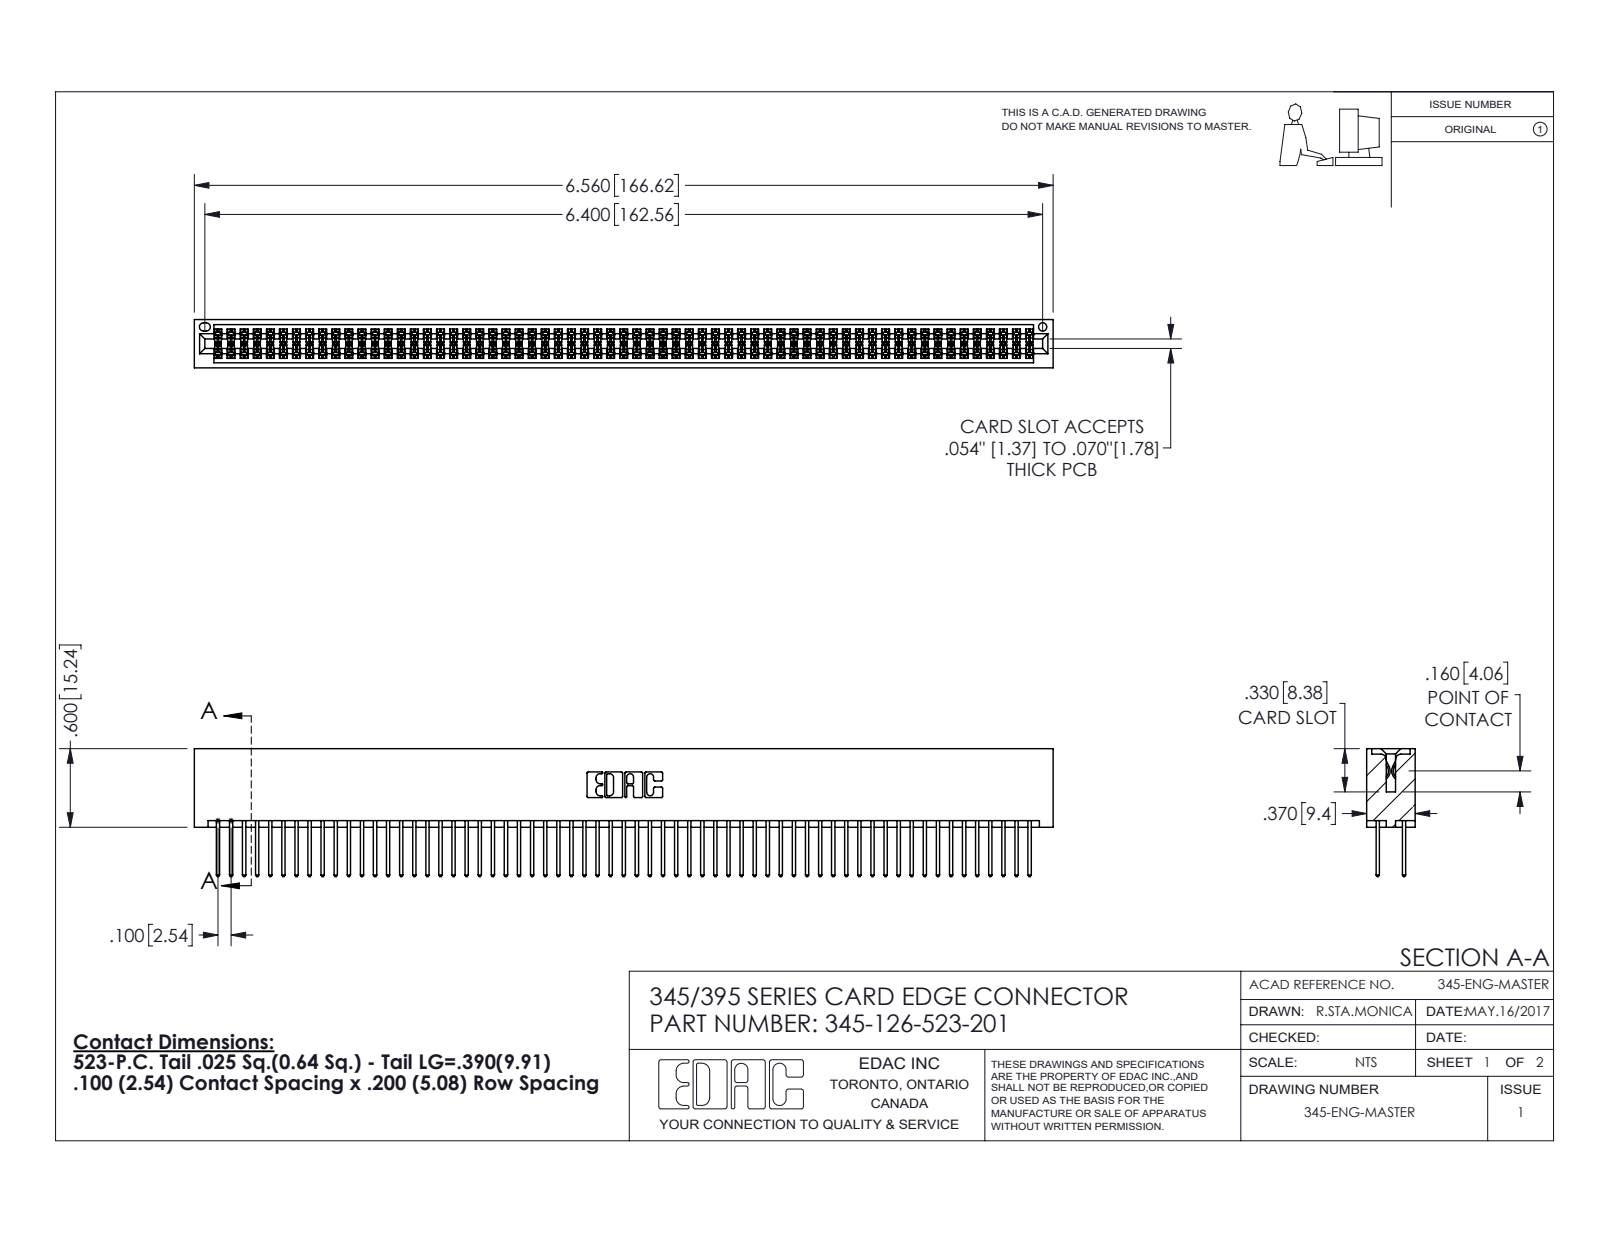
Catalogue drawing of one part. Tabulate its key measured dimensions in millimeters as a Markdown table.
| quantity | value |
| --- | --- |
| part name | 345-126-523-201; 345 Part_No Mounting Lugs; 345-292-001_345-293-123 |
| STEP written by | SolidWorks 2016 (CONFIG_CONTROL_DESIGN) |
| units | millimeters |
| bodies | 127 solids, 6418 faces (4234 planar, 2184 cylindrical, 0 other) |
| overall size | 166.6 × 24.8 × 9.4 |
| volume | 17 260 mm³ |
| surface area | 27 370 mm² |
| round holes (diameter × count) | 1.6 × 1 |
| partial cylindrical surfaces (radius × count) | 0.2 × 189, 0.3 × 126, 0.3 × 22, 0.2 × 6, 0.8 × 6, 0.7 × 3, 0.4 × 2, 0.5 × 2 |
| main face-to-face distances | 7.6, 1.8, 5.1, 2.5, 6.9, 0.6, 9.4, 5.7, 4.4, 3.8 |
